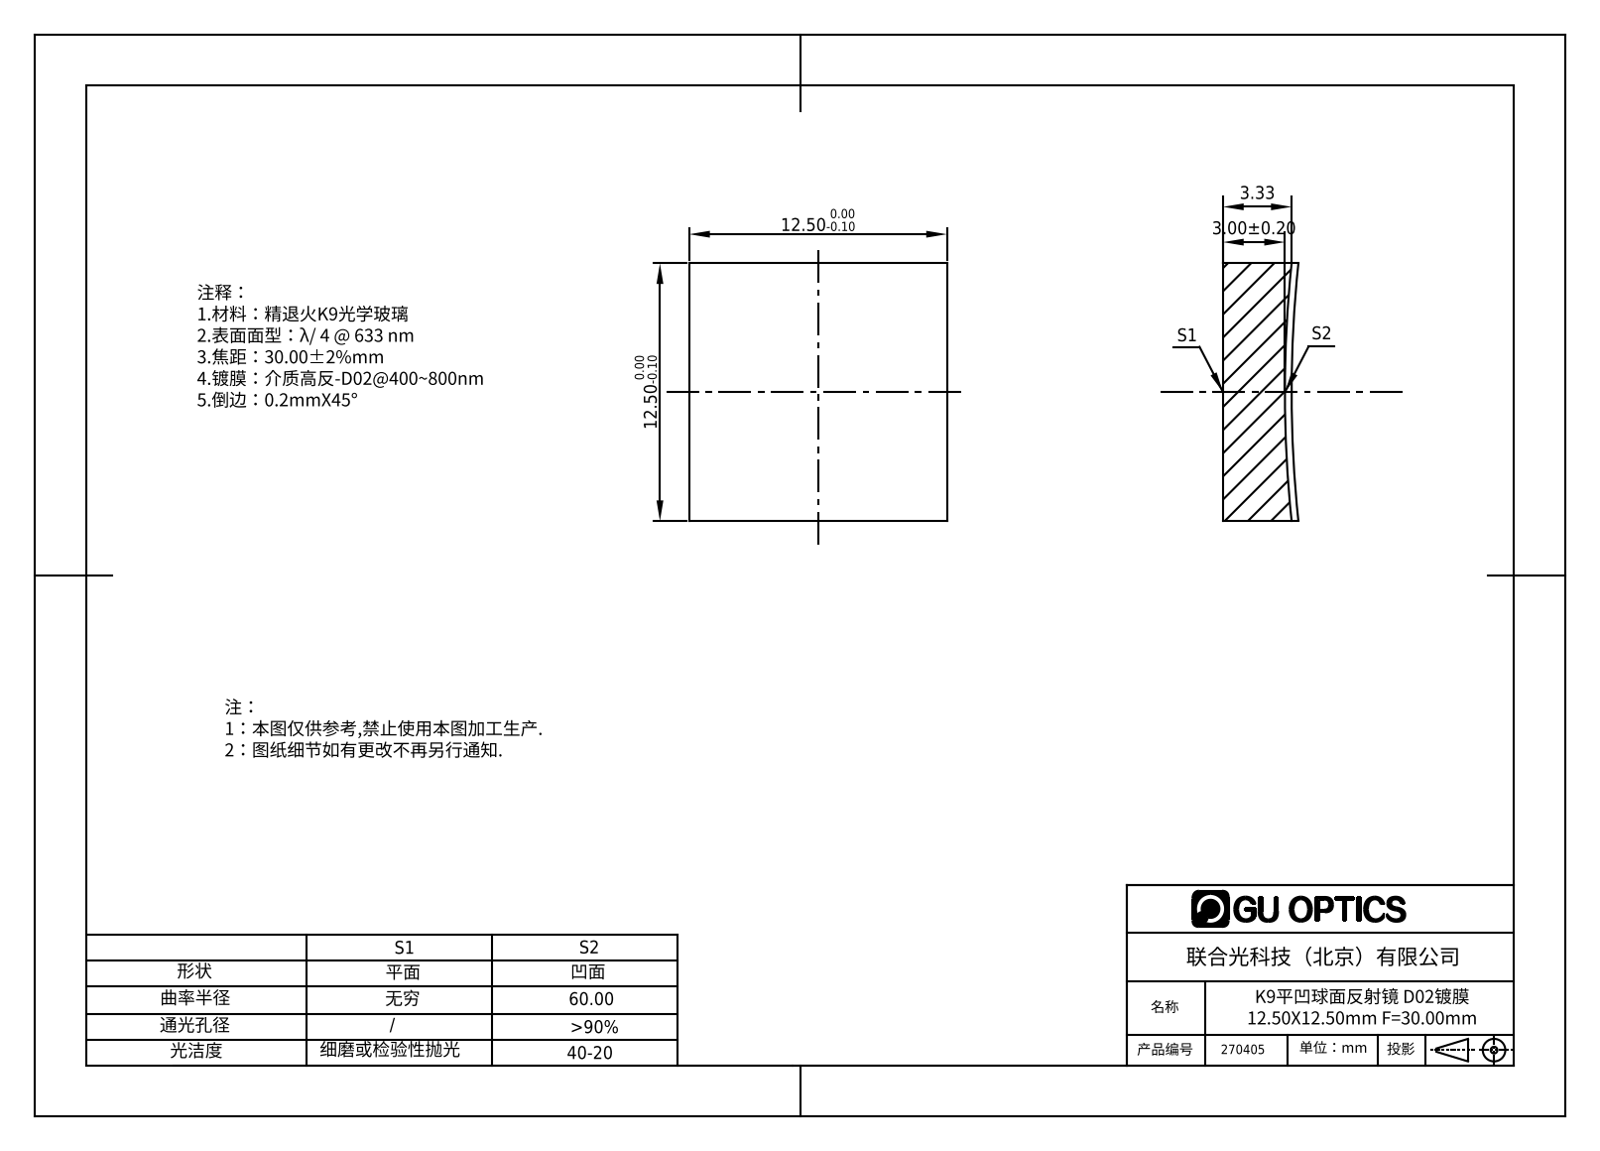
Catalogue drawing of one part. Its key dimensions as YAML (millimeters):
part_name: "270015"
step_written_by: "SolidWorks 2019 (AUTOMOTIVE_DESIGN)"
units: millimeters
bodies: {solids: 1, faces: 7, planar: 5, cylindrical: 0, other: 2}
overall_size: [12.5, 12.5, 3.65]
volume: 503
surface_area: 485
face_to_face_distances: [12.5]
